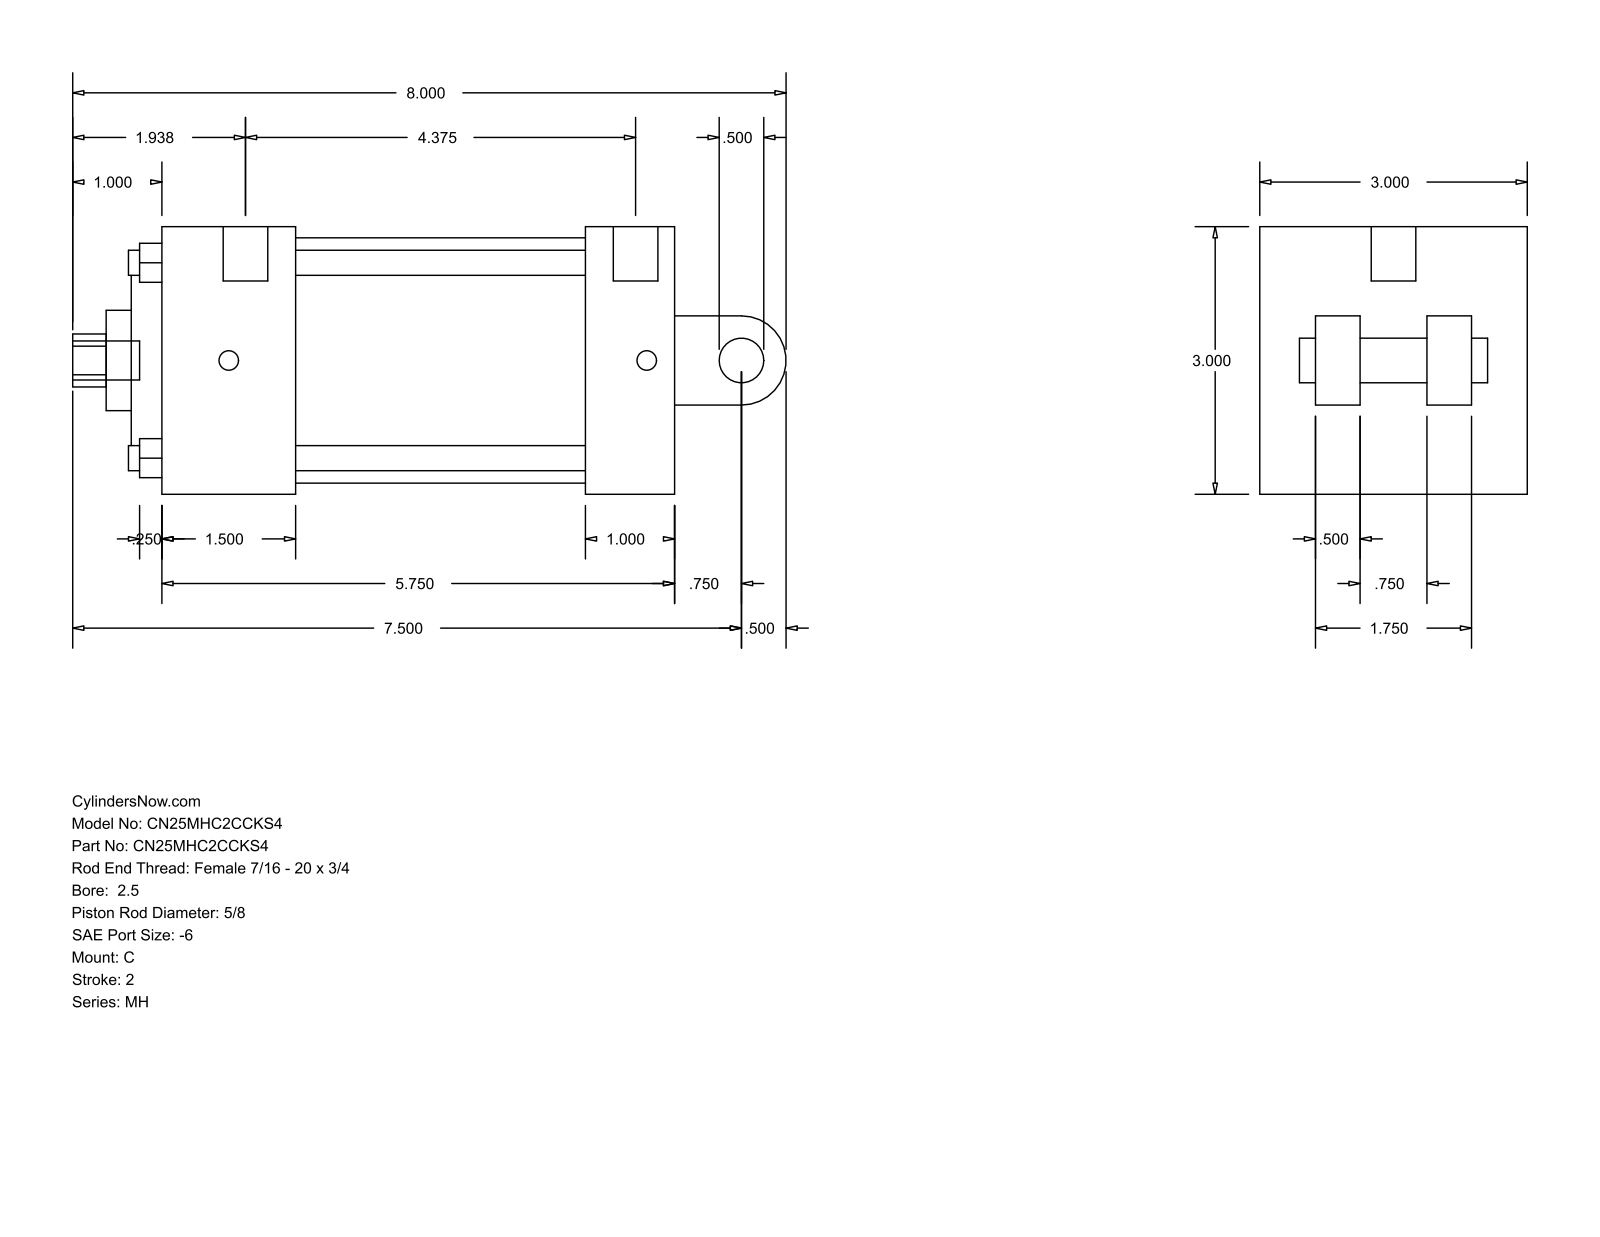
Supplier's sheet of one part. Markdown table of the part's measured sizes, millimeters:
| quantity | value |
| --- | --- |
| part name | MH_C__0250_0.625 |
| STEP written by | GSSL Pune (CONFIG_CONTROL_DESIGN) |
| units | millimeters |
| bodies | 0 solids, 101 faces (71 planar, 30 cylindrical, 0 other) |
| overall size | 203.2 × 76.2 × 76.2 |
| round holes (diameter × count) | 7.14 × 4, 5.56 × 2, 12.7 × 1, 15.88 × 1, 28.57 × 1, 55.55 × 1, 69.85 × 1 |
| round bosses / shafts (diameter × count) | 12.7 × 2, 5.56 × 2, 11.11 × 1 |
| partial cylindrical surfaces (radius × count) | 7.54 × 1, 12.7 × 1 |
| main face-to-face distances | 76.2, 25.4, 146.05, 15.87, 120.65, 38.1, 82.55, 107.95, 8.73, 46.83 |
| hole center spacings | 39.33, 55.62, 78.66, 3.17 |
